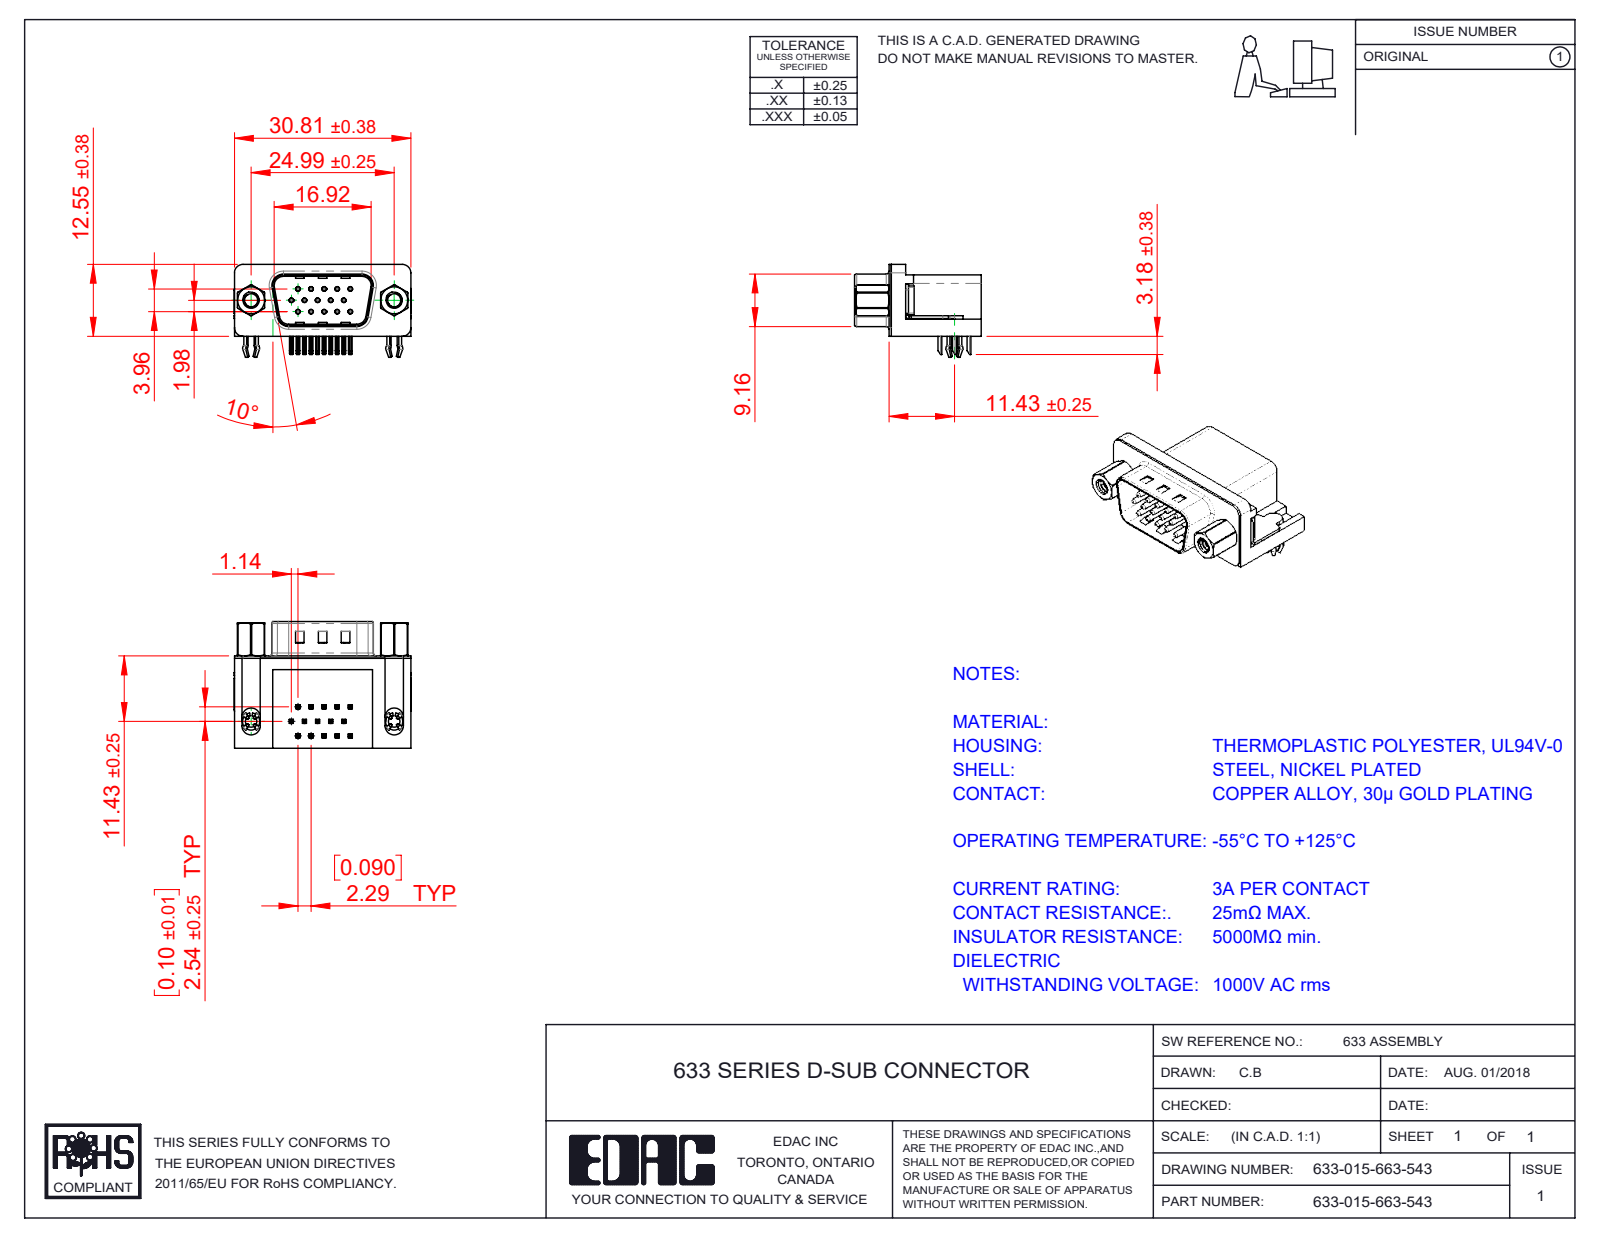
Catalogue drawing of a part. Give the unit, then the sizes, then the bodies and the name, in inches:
Units: inches
Overall size (bounding box): 1.216 × 0.87 × 0.64
Round holes (diameter × count): ⌀0.014 ×15, ⌀0.031 ×15, ⌀0.079 ×2, ⌀0.089 ×2, ⌀0.09 ×2, ⌀0.157 ×2, ⌀0.189 ×2, ⌀0.197 ×2
Round bosses / shafts (diameter × count): ⌀0.03 ×15, ⌀0.193 ×2, ⌀0.187 ×2, ⌀0.154 ×2, ⌀0.118 ×2, ⌀0.11 ×2
Partial cylindrical surfaces — rounded edges, fillets, slot ends (radius × count): R0.01 ×72, R0.005 ×30, R0.039 ×16, R0.02 ×9, R0.063 ×8, R0.059 ×7, R0.035 ×4, R0.079 ×4
Main face-to-face distances: 0.016, 0.407, 0.618, 0.634, 0.114, 0.098, 0.264, 0.02, 0.014, 0.421
Hole centre spacings: 0.156, 0.09, 0.18, 0.09, 0.238, 0.27, 0.312, 0.238
Volume: 0.261 in³ · Surface area: 9.226 in²
Bodies: 23 solids, 1683 faces (925 planar, 513 cylindrical, 245 other)
Part name (STEP PRODUCT): 633-015-663-543; 633 Contact Top; 633 4 Prong Board Lock; 633 Shell_15 Contact (+5 more)
STEP written by: SolidWorks 2016 (CONFIG_CONTROL_DESIGN)
